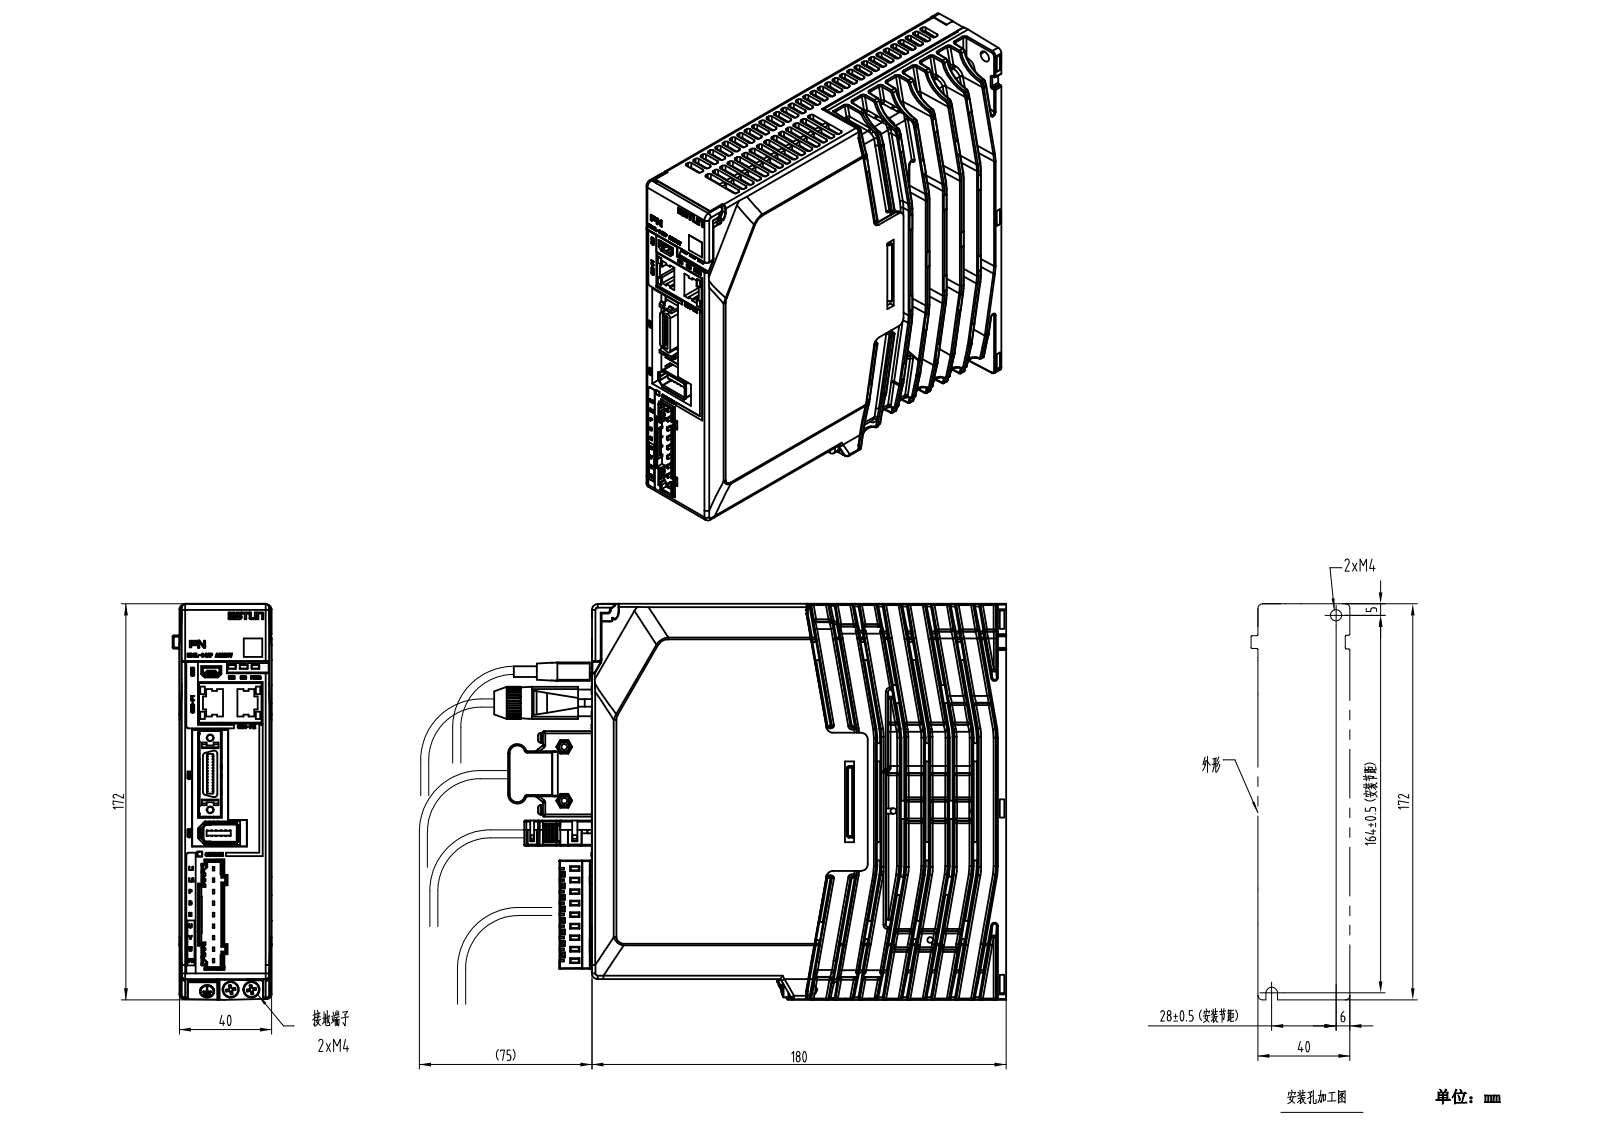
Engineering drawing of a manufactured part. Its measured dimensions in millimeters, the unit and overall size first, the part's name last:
Units: millimetres
Overall size (bounding box): 181 × 172 × 43
Round holes (diameter × count): ⌀2 ×7, ⌀2.5 ×7, ⌀3.5 ×7, ⌀3.2 ×6, ⌀3.4 ×6, ⌀1.2 ×3, ⌀2.2 ×3, ⌀8 ×3, ⌀1.25 ×2, ⌀2.05 ×2, ⌀2.6 ×2, ⌀2.8 ×2
Round bosses / shafts (diameter × count): ⌀1 ×16, ⌀0.5 ×10, ⌀7 ×6, ⌀5.6 ×6, ⌀5 ×6, ⌀4 ×6, ⌀3 ×6, ⌀2.3 ×4
Partial cylindrical surfaces — rounded edges, fillets, slot ends (radius × count): R1 ×289, R0.5 ×282, R0.3 ×146, R0.15 ×103, R0.2 ×76, R1.5 ×27, R4 ×26, R0.9 ×21
Main face-to-face distances: 2, 8.5, 6.5, 31.5, 33.5, 40, 10.5, 23, 8.3, 6.3
Hole centre spacings: 9.12, 34.69, 6.5, 148, 4.74, 5, 6.14, 12.36
Volume: 345 577 mm³ · Surface area: 284 667 mm²
Bodies: 45 solids, 9936 faces (6127 planar, 1912 cylindrical, 1897 other)
Part name (STEP PRODUCT): A结构PN
STEP written by: SolidWorks 2018 (CONFIG_CONTROL_DESIGN)
